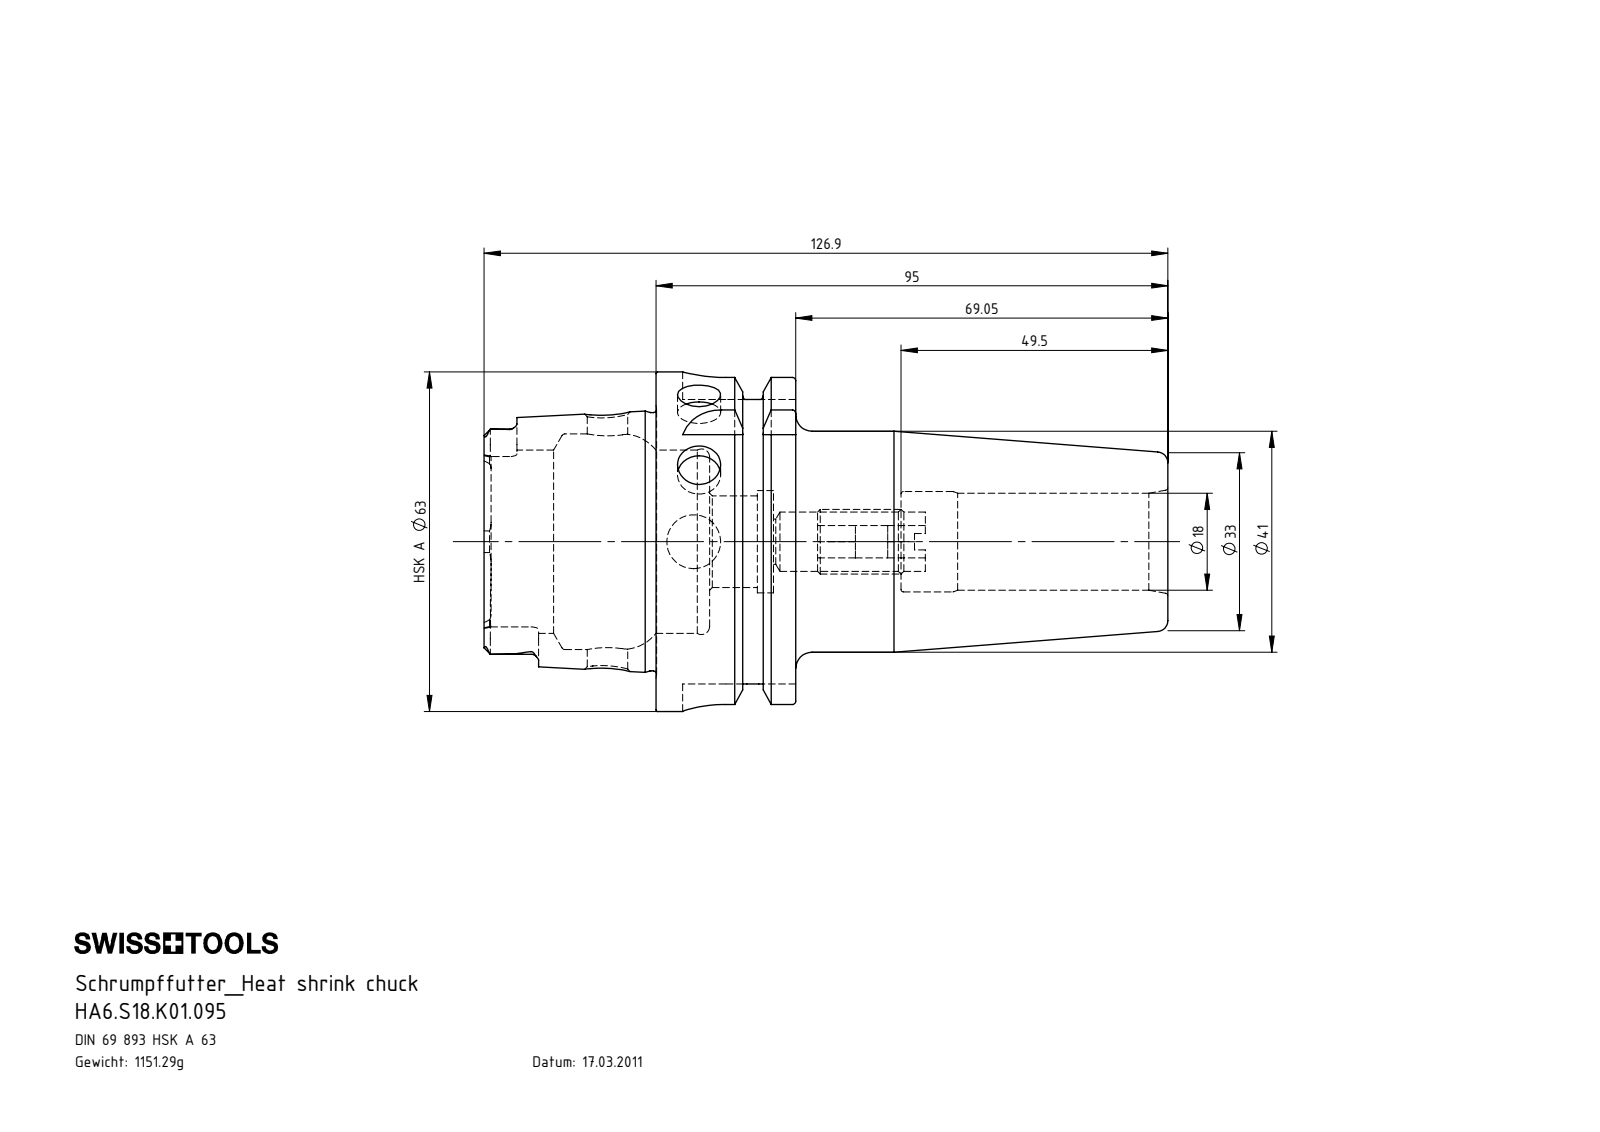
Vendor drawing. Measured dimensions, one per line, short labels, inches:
name: HA6-S18.K01.095; ERU-AN5.K01.020_A; HA6-S18.K01.095_B_Fertigbearbeitung
written by: SolidWorks 2012 (AUTOMOTIVE_DESIGN)
unit: in
bodies: 2 solids, 232 faces (82 planar, 61 cylindrical, 89 other)
size: 4.996 × 2.48 × 2.48
volume: 8.95 in³; area: 53.85 in²
holes: 2× ⌀0.315, 1× ⌀0.236, 1× ⌀0.295, 1× ⌀0.331, 1× ⌀0.394, 1× ⌀0.433, 1× ⌀0.669, 1× ⌀0.709, 1× ⌀0.732, 1× ⌀0.748, 1× ⌀1.339, 1× ⌀1.575
bosses: 1× ⌀2.48, 1× ⌀2.163, 1× ⌀1.887, 1× ⌀1.614, 1× ⌀0.472
rounds: 6× R0.055, 4× R0.113, 4× R0.315
face distances: 1.022, 0.63, 0.392, 3.74, 3.348, 2.719, 1.256, 1.648, 2.278, 4.996
